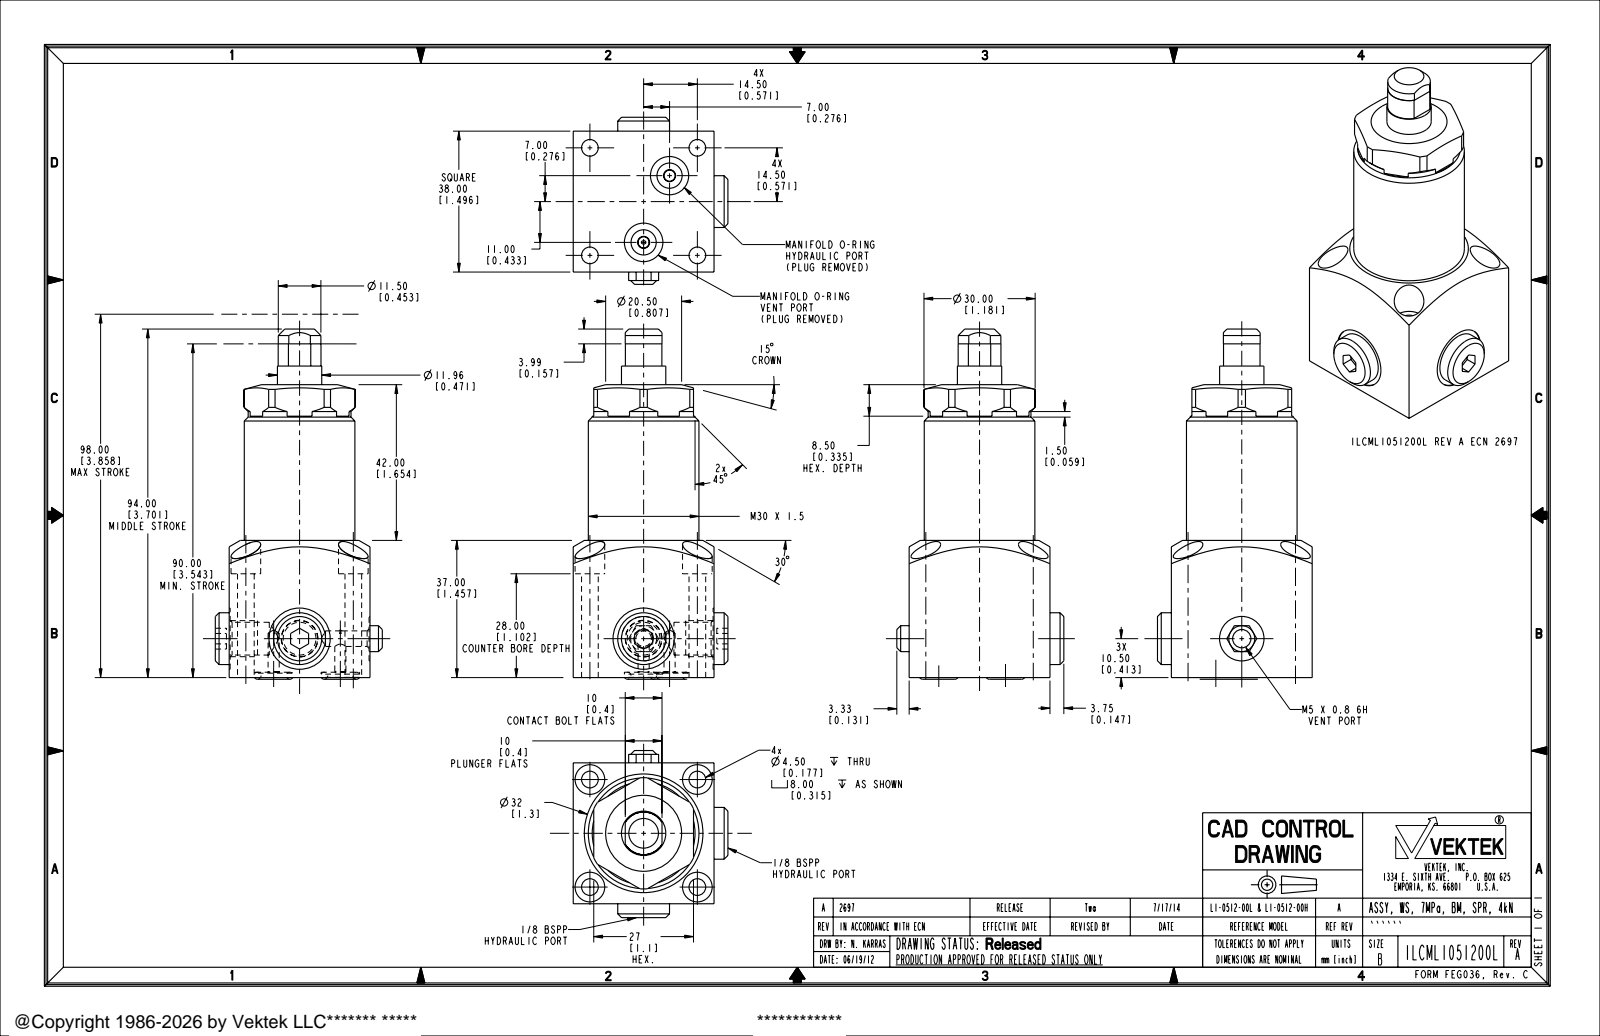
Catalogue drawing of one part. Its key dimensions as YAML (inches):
part_name: "ILCML1051200L"
step_written_by: "PRO/ENGINEER BY PARAMETRIC TECHNOLOGY CORPORATION, 2013320 (AUTOMOTIVE_DESIGN)"
units: inches
bodies: {solids: 1, faces: 182, planar: 72, cylindrical: 64, other: 46}
overall_size: [3.719, 1.774, 1.644]
volume: 4.78
surface_area: 26.32
round_holes:
  - {diameter: 0.177, count: 4}
  - {diameter: 0.315, count: 4}
  - {diameter: 0.118, count: 2}
  - {diameter: 0.348, count: 2}
  - {diameter: 0.65, count: 2}
  - {diameter: 0.165, count: 1}
  - {diameter: 0.394, count: 1}
  - {diameter: 0.409, count: 1}
  - {diameter: 0.472, count: 1}
round_bosses_or_shafts:
  - {diameter: 0.55, count: 2}
  - {diameter: 0.383, count: 2}
  - {diameter: 1.175, count: 1}
  - {diameter: 1.093, count: 1}
  - {diameter: 0.471, count: 1}
partial_cylinders:
  - {radius: 0.226, count: 1}
  - {radius: 0.228, count: 1}
  - {radius: 0.591, count: 1}
face_to_face_distances: [1.496, 1.486, 1.06, 3.11, 1.644, 0.157, 0.148, 0.218, 1.278, 0.057]
hole_center_spacings: [1.142, 0.587, 0.896, 1.155, 1.615, 0.418, 0.76, 1.197]
